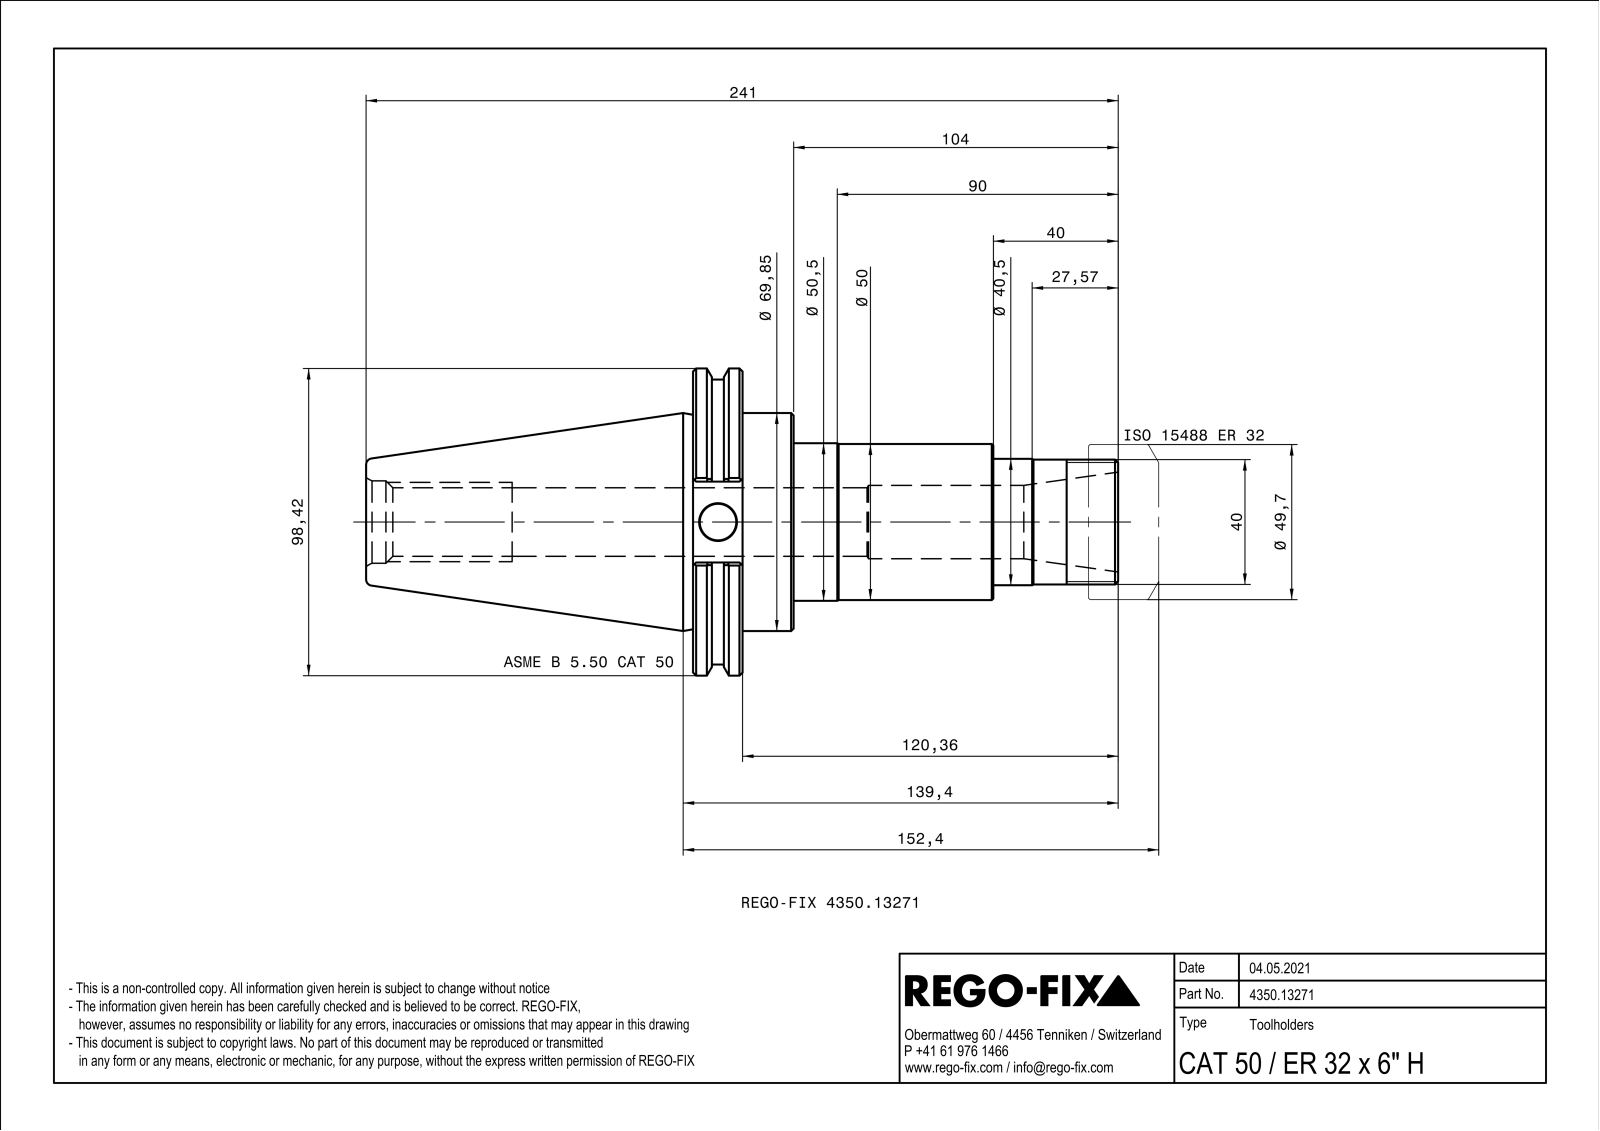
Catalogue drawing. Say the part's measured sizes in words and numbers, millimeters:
The part is named "NOCUT". Its 3-D file was written by "SIEMENS PLM Software Solid Edge ST10 (AUTOMOTIVE_DESIGN)". It is 1 solid with 126 faces: 33 planar, 35 cylindrical and 58 other. Overall it measures 241 by 98.42 by 94.39 millimeters. Its volume is 500 626 cubic millimeters and its surface area 71 107 square millimeters. Round holes: 1 of diameter 11.7, 1 of diameter 21.96, 1 of diameter 21.96, 1 of diameter 23.5, 1 of diameter 26.4. Round bosses or shafts: 1 of diameter 98.42, 1 of diameter 91.3, 1 of diameter 69.85, 1 of diameter 50.5, 1 of diameter 50, 1 of diameter 40.5, 1 of diameter 40. Partial cylindrical surfaces (rounded edges, fillets, slot ends): 12 of radius 0.5. The main face-to-face distances are 15.87, 16.36, 32.23, 64, 80.36, 96.23, 201, 137, 120.64, 104.77.
